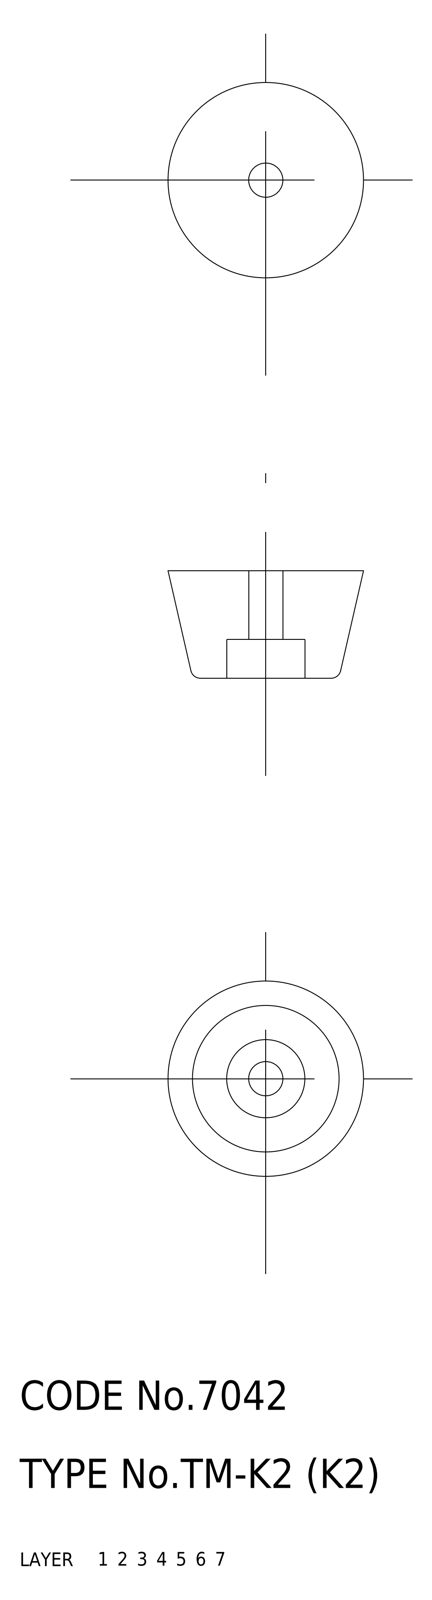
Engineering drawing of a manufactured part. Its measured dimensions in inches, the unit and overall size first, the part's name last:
Units: inches
Overall size (bounding box): 0.787 × 0.787 × 0.433
Volume: 0.146 in³ · Surface area: 1.95 in²
Bodies: 1 solid, 11 faces (0 planar, 0 cylindrical, 11 other)
Part name (STEP PRODUCT): rubber foot
STEP written by: CADfix (AUTOMOTIVE_DESIGN)
